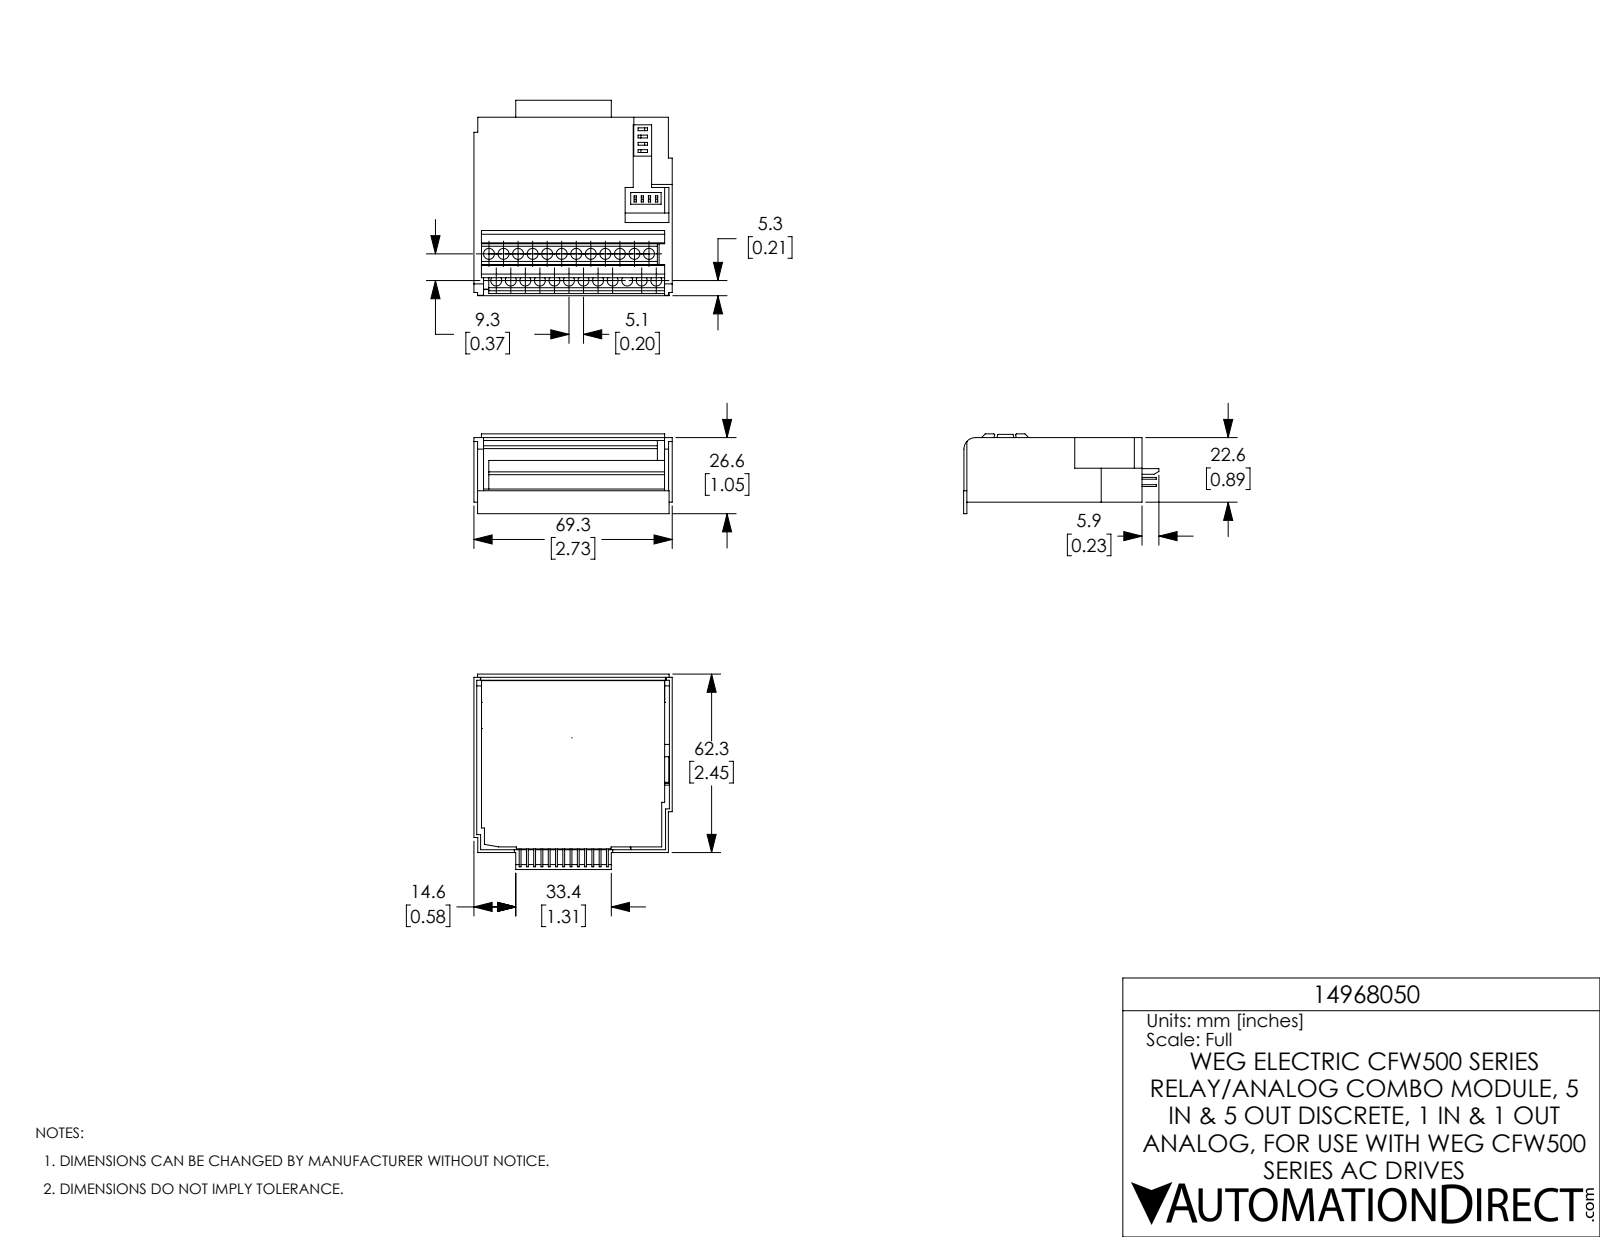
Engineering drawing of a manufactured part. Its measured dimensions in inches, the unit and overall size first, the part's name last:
Units: inches
Overall size (bounding box): 2.726 × 2.685 × 1.096
Round holes (diameter × count): ⌀0.15 ×24
Partial cylindrical surfaces — rounded edges, fillets, slot ends (radius × count): R0.118 ×1, R0.157 ×1
Main face-to-face distances: 0.039, 0.73, 0.063, 0.667, 0.77, 0.707, 2.687, 2.727, 0.051, 1.704
Hole centre spacings: 0.38, 0.2, 0.474, 0.4, 0.62, 0.6, 0.79, 0.8
Volume: 1.904 in³ · Surface area: 46.68 in²
Bodies: 1 solid, 437 faces (385 planar, 52 cylindrical, 0 other)
Part name (STEP PRODUCT): 14968050_MODULO IO CFW500_IOR_B Coord nc
STEP written by: SolidWorks 2017 (AUTOMOTIVE_DESIGN)
